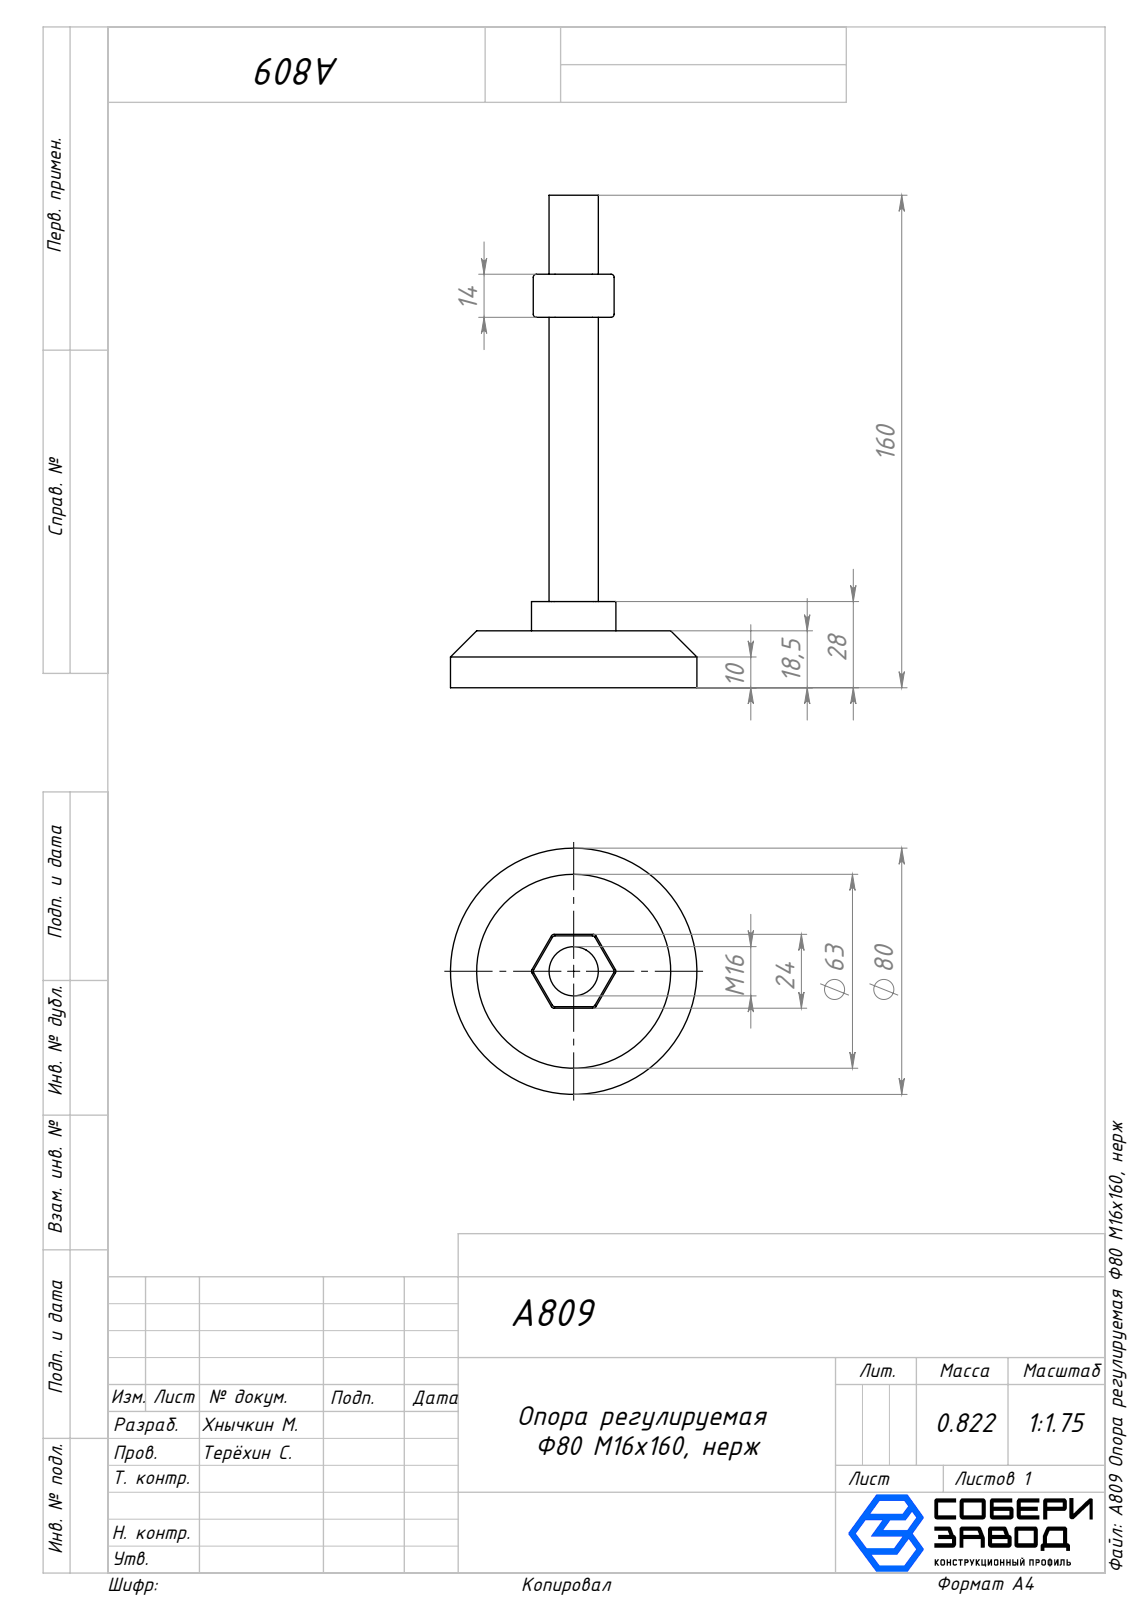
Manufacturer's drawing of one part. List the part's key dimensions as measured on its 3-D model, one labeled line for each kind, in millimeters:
Part name (STEP PRODUCT): hex bolt gradeab_din_DIN EN 24014 - M5 x 25 x 16-N; A809 Опора регулируемая Ф80 М16х160, нерж; Гайка М16_00; Опора_00 (+1 more)
STEP written by: SolidWorks 2025 (AUTOMOTIVE_DESIGN)
Units: millimetres
Bodies: 4 solids, 110 faces (36 planar, 44 cylindrical, 30 other)
Overall size (bounding box): 160 × 80 × 80
Volume: 116 376 mm³ · Surface area: 26 254 mm²
Round holes (diameter × count): ⌀5.2 ×1, ⌀14 ×1, ⌀27 ×1
Round bosses / shafts (diameter × count): ⌀80 ×1, ⌀16 ×1, ⌀8 ×1, ⌀5 ×1
Partial cylindrical surfaces — rounded edges, fillets, slot ends (radius × count): R1 ×24
Main face-to-face distances: 18.5, 0.5, 23.5, 23, 7, 11.5, 24, 28, 21, 9.5
